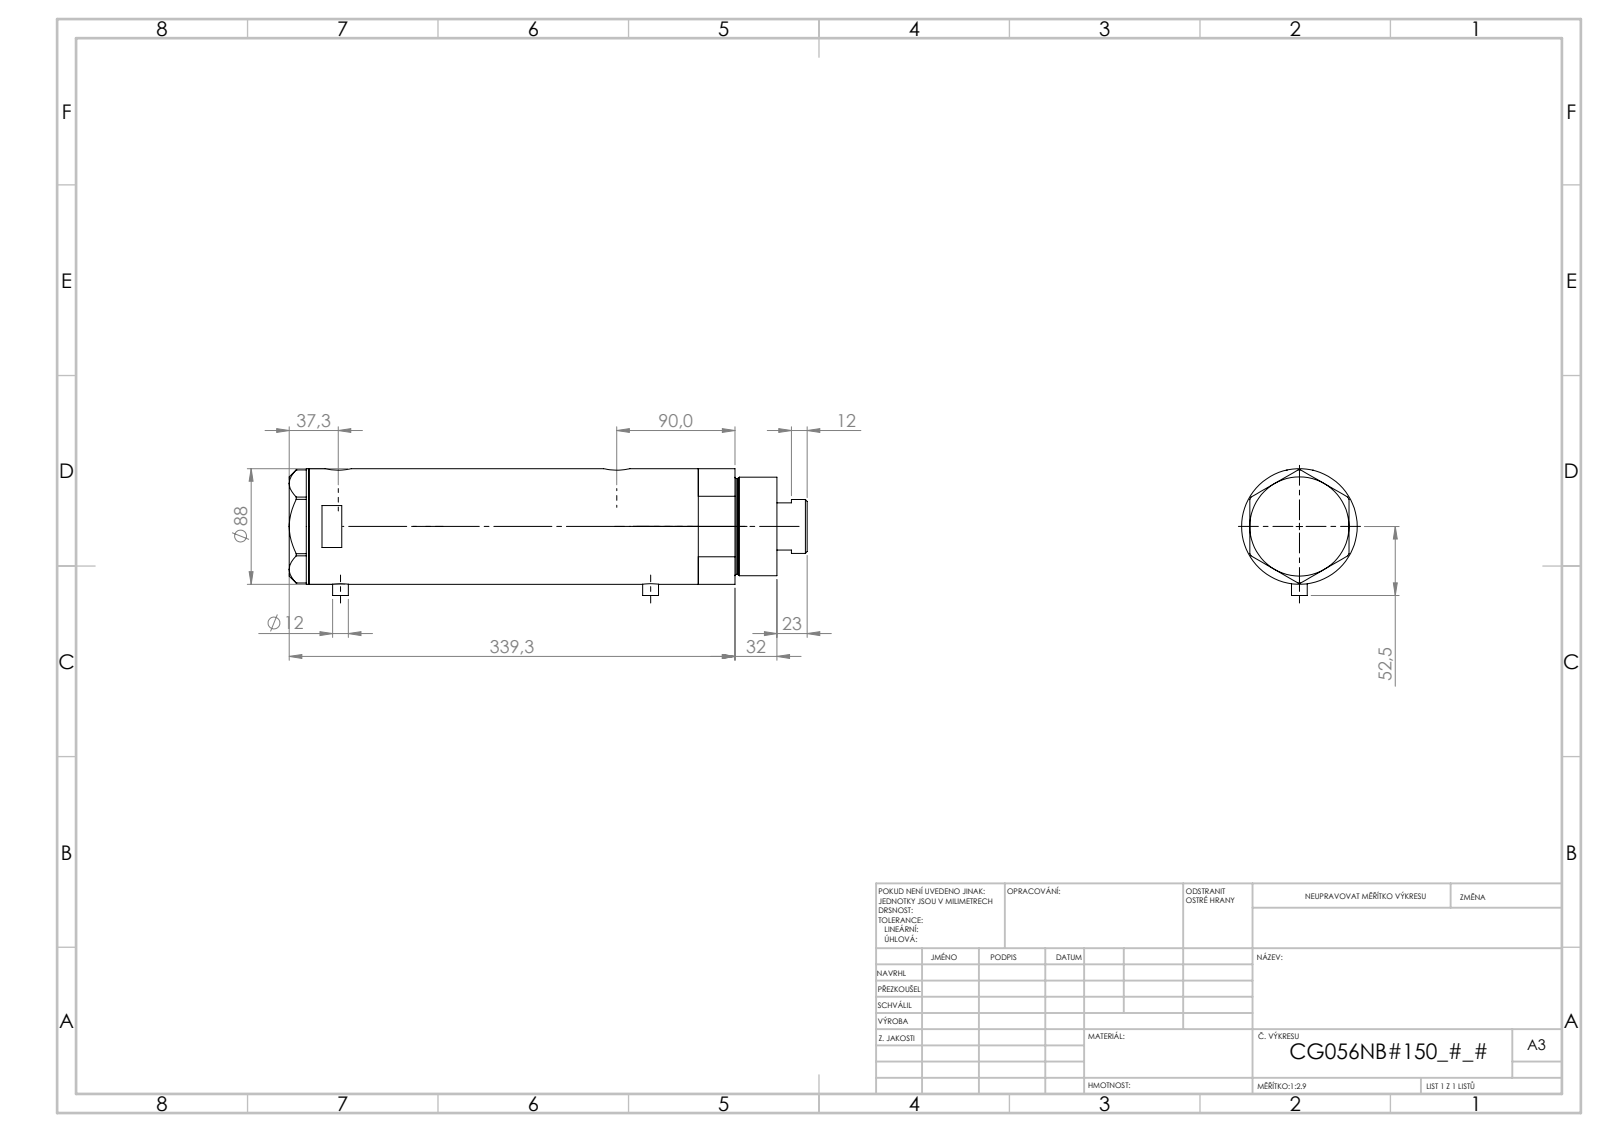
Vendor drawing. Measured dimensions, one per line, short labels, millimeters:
name: V270CG_FRONT; V270CG_BACK; V270CG_VC; V270CG_MIDDLE
written by: SolidWorks 2019 (CONFIG_CONTROL_DESIGN)
unit: mm
bodies: 4 solids, 126 faces (53 planar, 53 cylindrical, 20 other)
size: 374.47 × 89.1 × 88
volume: 1 913 000 mm³; area: 267 910 mm²
holes: 2× ⌀5, 2× ⌀12.5, 2× ⌀13.16, 2× ⌀20, 1× ⌀14.5, 1× ⌀42, 1× ⌀43.5, 1× ⌀56, 1× ⌀60, 1× ⌀80
bosses: 2× ⌀12, 1× ⌀88, 1× ⌀75, 1× ⌀73, 1× ⌀41
face distances: 224.4, 26, 198.4, 15, 41, 239.4, 336.47, 351.47, 310.47, 112.07
hole spacings: 1.7, 25.8, 200.3, 202, 226.1, 227.8
